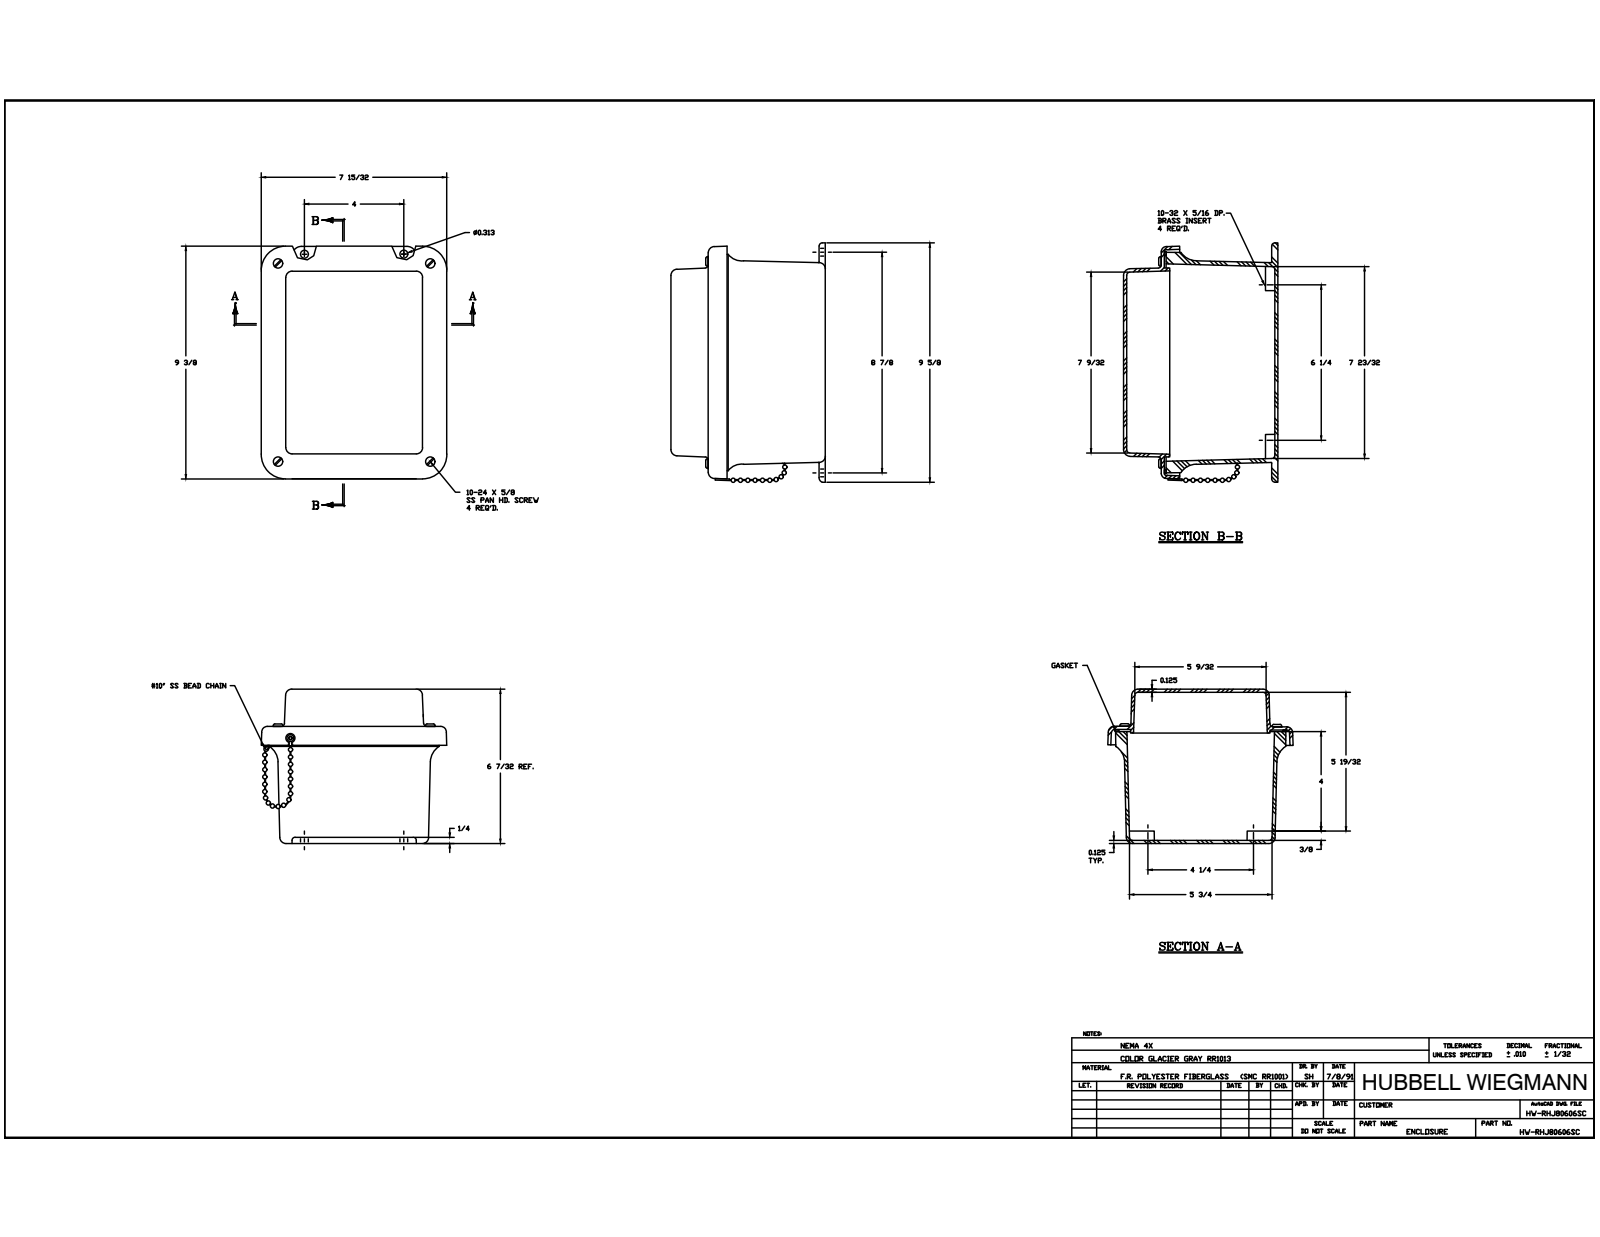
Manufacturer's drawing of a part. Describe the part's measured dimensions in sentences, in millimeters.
The part is named "J806W_2; RMINS45821P_73; RMINS45821P_74; RMINS45821P_75 (+8 more)". Its 3-D file was written by "Autodesk Inventor 2014 (AUTOMOTIVE_DESIGN)". It is 21 solids with 920 faces: 213 planar, 298 cylindrical and 409 other. Overall it measures 257.18 by 197.05 by 157.46 millimeters. Its volume is 789 358 cubic millimeters and its surface area 425 304 square millimeters. Round holes: 5 of diameter 3.86, 4 of diameter 3.56, 4 of diameter 3.68, 4 of diameter 3.96, 4 of diameter 5.54, 2 of diameter 4.76, 1 of diameter 3.2. Round bosses or shafts: 8 of diameter 6.86, 4 of diameter 4.83, 4 of diameter 3.97, 2 of diameter 9.52, 2 of diameter 6.35, 2 of diameter 3.17, 1 of diameter 7.19. Partial cylindrical surfaces (rounded edges, fillets, slot ends): 20 of radius 0.79, 20 of radius 3.17, 12 of radius 6.35, 4 of radius 5.08, 4 of radius 7.86, 4 of radius 7.94, 4 of radius 9.53, 4 of radius 19.48. The main face-to-face distances are 3.17, 3.18, 38.48, 151.1, 112.62, 154.28, 157.45, 154.27, 115.8, 41.65. The hole center spacings are 33.68, 133.89, 184.12, 225.15, 107.94, 155.58, 158.76, 191.98.
